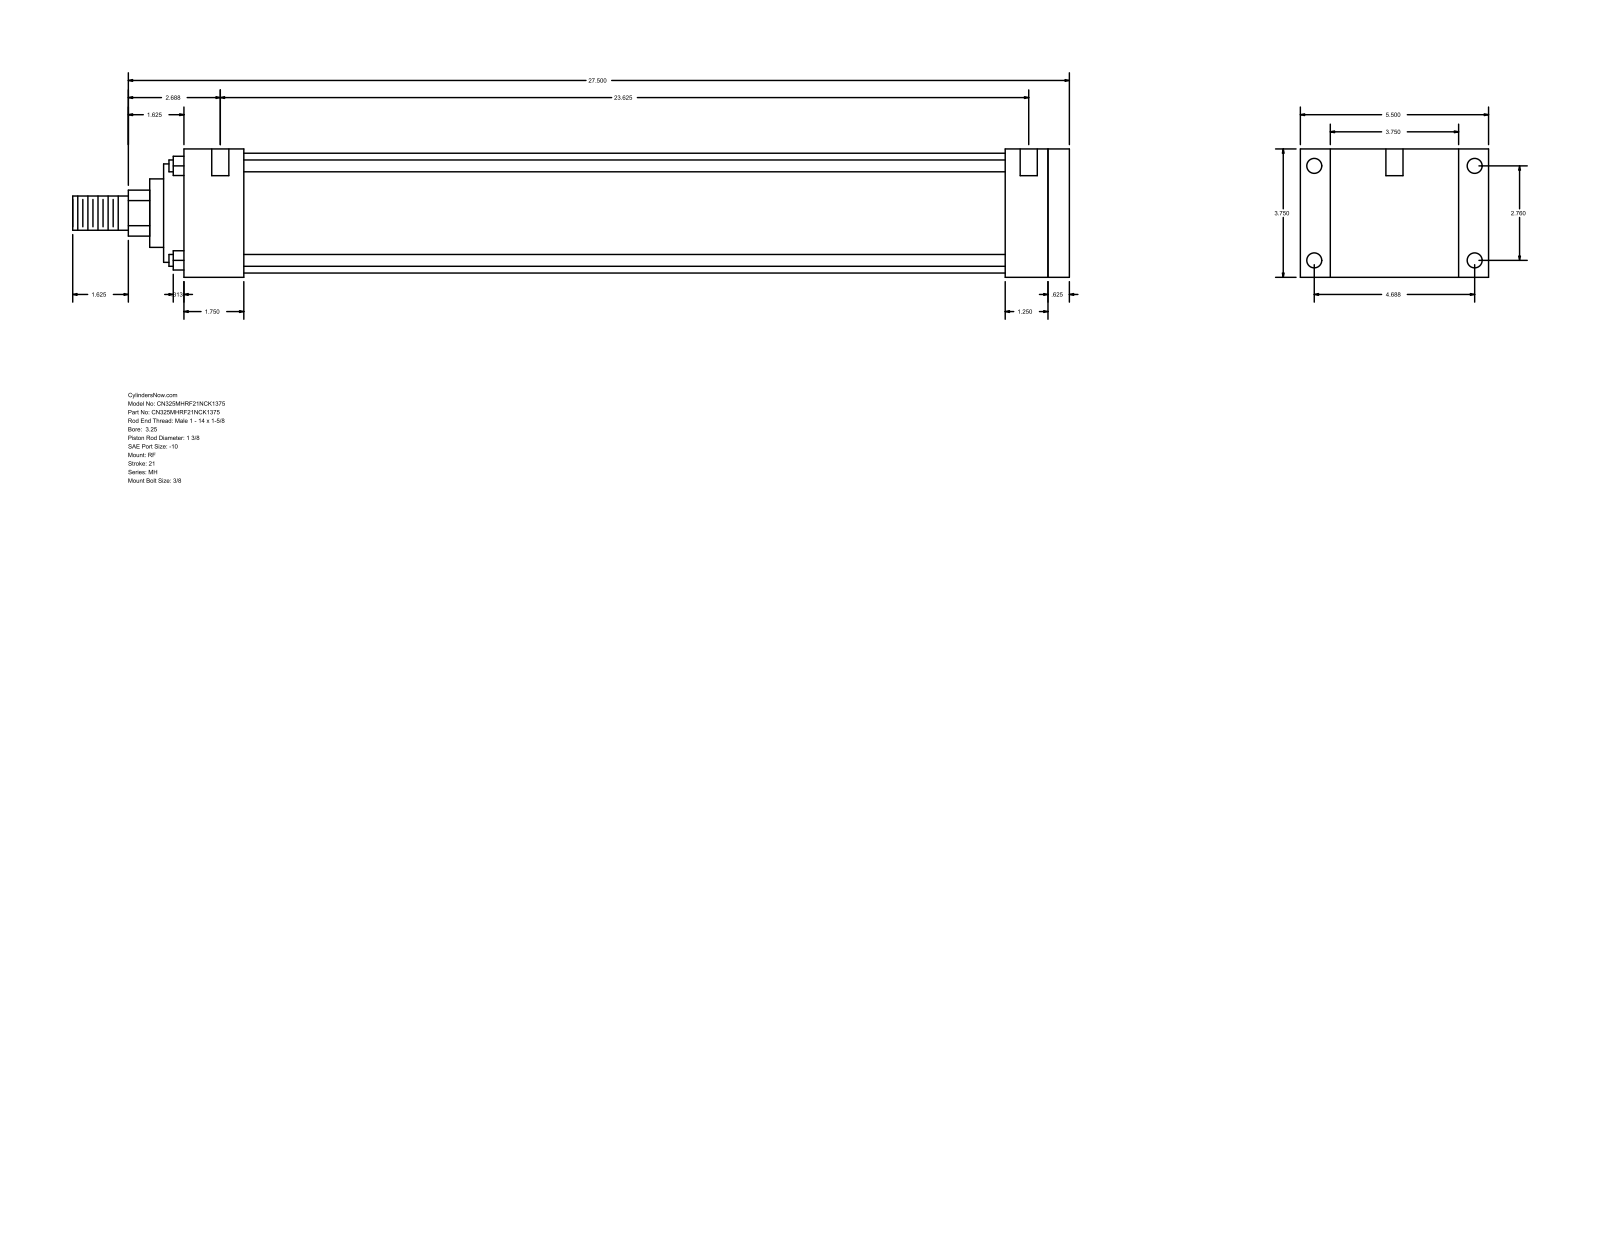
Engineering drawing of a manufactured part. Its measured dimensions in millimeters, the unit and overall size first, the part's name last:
Units: millimetres
Overall size (bounding box): 739.77 × 139.7 × 95.25
Round holes (diameter × count): ⌀5.56 ×4, ⌀11.13 ×4, ⌀12.7 ×2
Round bosses / shafts (diameter × count): ⌀8.76 ×4, ⌀88.9 ×1, ⌀73.03 ×1, ⌀50.8 ×1, ⌀34.92 ×1, ⌀25.4 ×1
Partial cylindrical surfaces — rounded edges, fillets, slot ends (radius × count): R17.06 ×1
Main face-to-face distances: 95.24, 657.23, 15.88, 641.35, 22.23, 117.47, 44.45, 596.9, 612.78, 609.61
Hole centre spacings: 70.1, 119.06, 138.16, 606.43, 1.59, 4.76, 600.08, 601.67
Bodies: 0 solids, 94 faces (65 planar, 29 cylindrical, 0 other)
Part name (STEP PRODUCT): MH_RF__0325_1.375
STEP written by: GSSL Pune (CONFIG_CONTROL_DESIGN)
